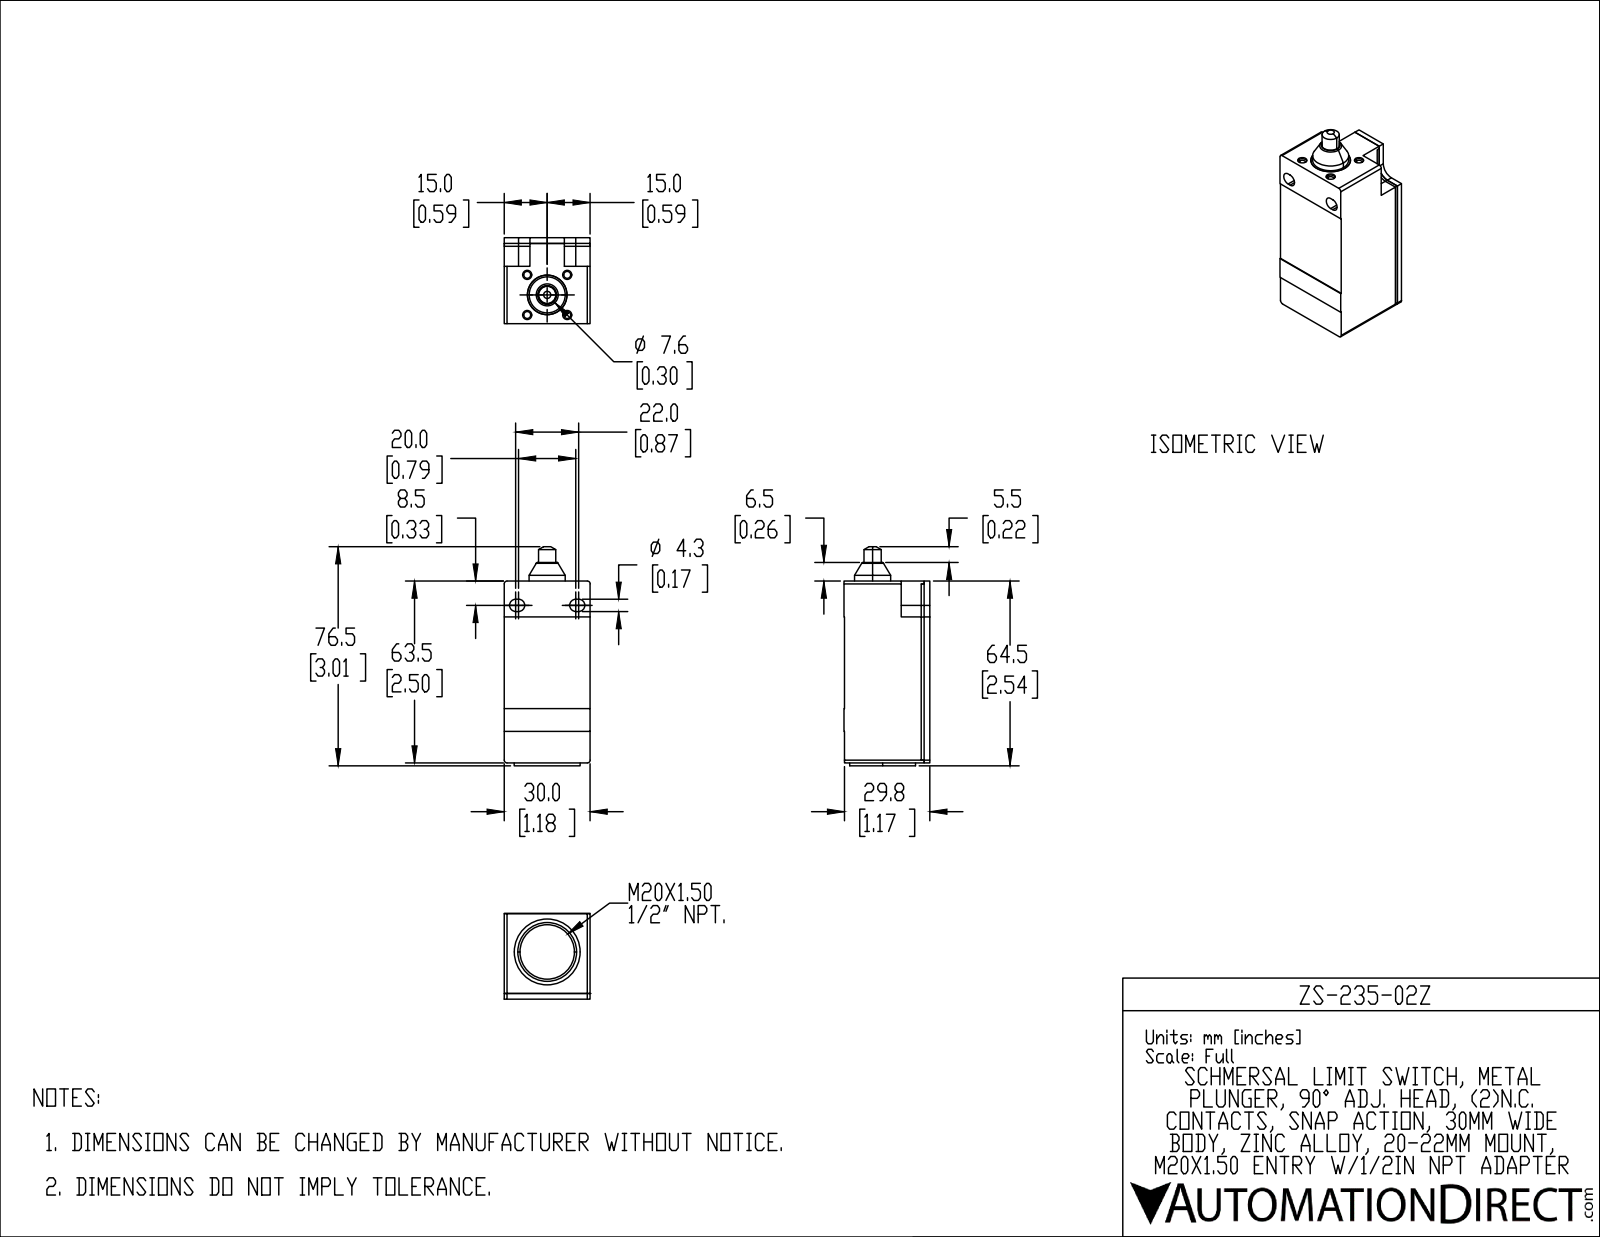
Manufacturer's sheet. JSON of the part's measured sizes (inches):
{"part_name": "ZS-235-02Z", "step_written_by": "SolidWorks 2019 (AUTOMOTIVE_DESIGN)", "units": "inches", "bodies": {"solids": 1, "faces": 196, "planar": 110, "cylindrical": 70, "other": 16}, "overall_size": [3.012, 1.181, 1.181], "volume_in3": 3.231, "surface_area_in2": 17.77, "round_holes": [[0.094, 4], [0.126, 4], [0.276, 3], [0.244, 1], [0.545, 1], [0.748, 1]], "round_bosses_or_shafts": [[0.256, 3], [0.906, 1], [0.543, 1], [0.496, 1], [0.236, 1]], "partial_cylinders_radius": [[0.02, 12], [0.039, 4], [0.085, 4], [0.157, 2], [0.159, 2]], "face_to_face_distances": [1.181, 1.173, 2.5, 0.207, 2.293, 0.354, 0.039, 0.787, 0.394, 0.78], "hole_center_spacings": [0.39, 0.551, 0.308, 0.497, 0.78, 2.228, 0.138, 0.866]}
